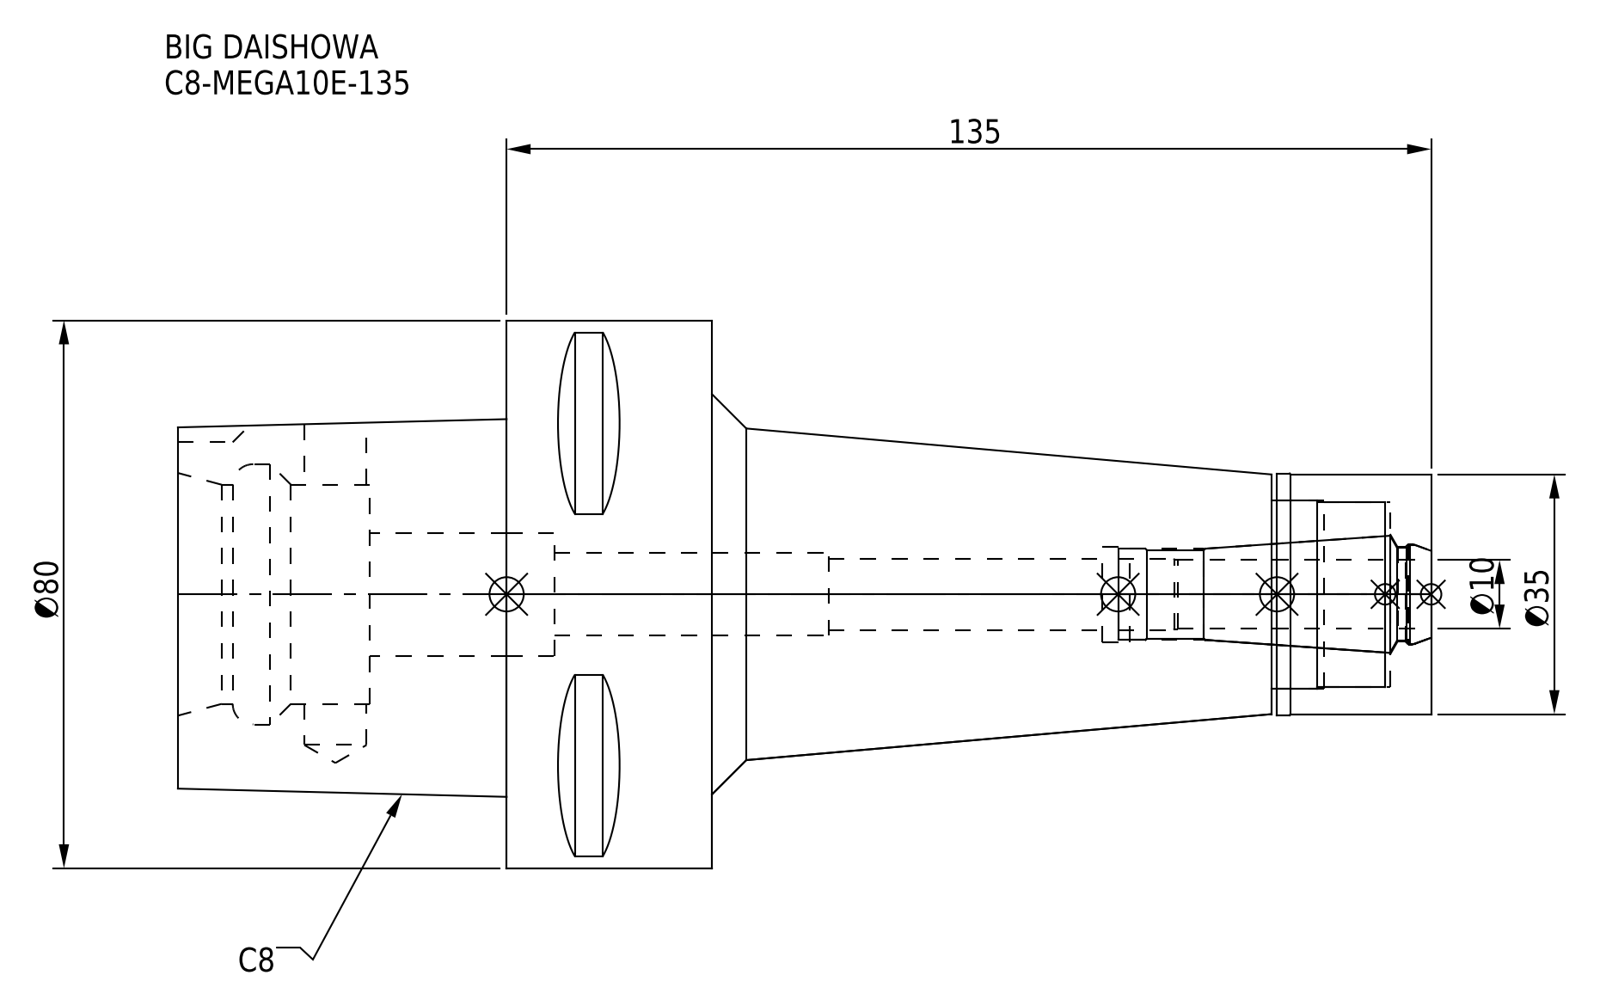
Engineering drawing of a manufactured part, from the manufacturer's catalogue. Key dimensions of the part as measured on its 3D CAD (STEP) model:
Part name (STEP PRODUCT): MEN10_1.stp; C8-MEGA10E-135-100-FreeParts; C8-MEGA10E-135-100_ASM.stp; DXF_TEMP_ASSY_ASM_4_ASM.stp (+3 more)
STEP written by: SolidWorks 2019 (CONFIG_CONTROL_DESIGN)
Units: millimetres
Bodies: 2 solids, 100 faces (37 planar, 39 cylindrical, 24 other)
Overall size (bounding box): 183 × 80 × 80
Volume: 346 062 mm³ · Surface area: 52 282 mm²
Round holes (diameter × count): ⌀9.1 ×1, ⌀10.4 ×1, ⌀12 ×1, ⌀13.3 ×1, ⌀13.8 ×1, ⌀13.9 ×1, ⌀14.7 ×1, ⌀18 ×1, ⌀27 ×1, ⌀27.5 ×1, ⌀32 ×1, ⌀38 ×1
Round bosses / shafts (diameter × count): ⌀80 ×1, ⌀35.3 ×1, ⌀35 ×1
Partial cylindrical surfaces — rounded edges, fillets, slot ends (radius × count): R6 ×1
Main face-to-face distances: 30, 48, 78, 135, 105, 183, 20, 155, 50, 28
